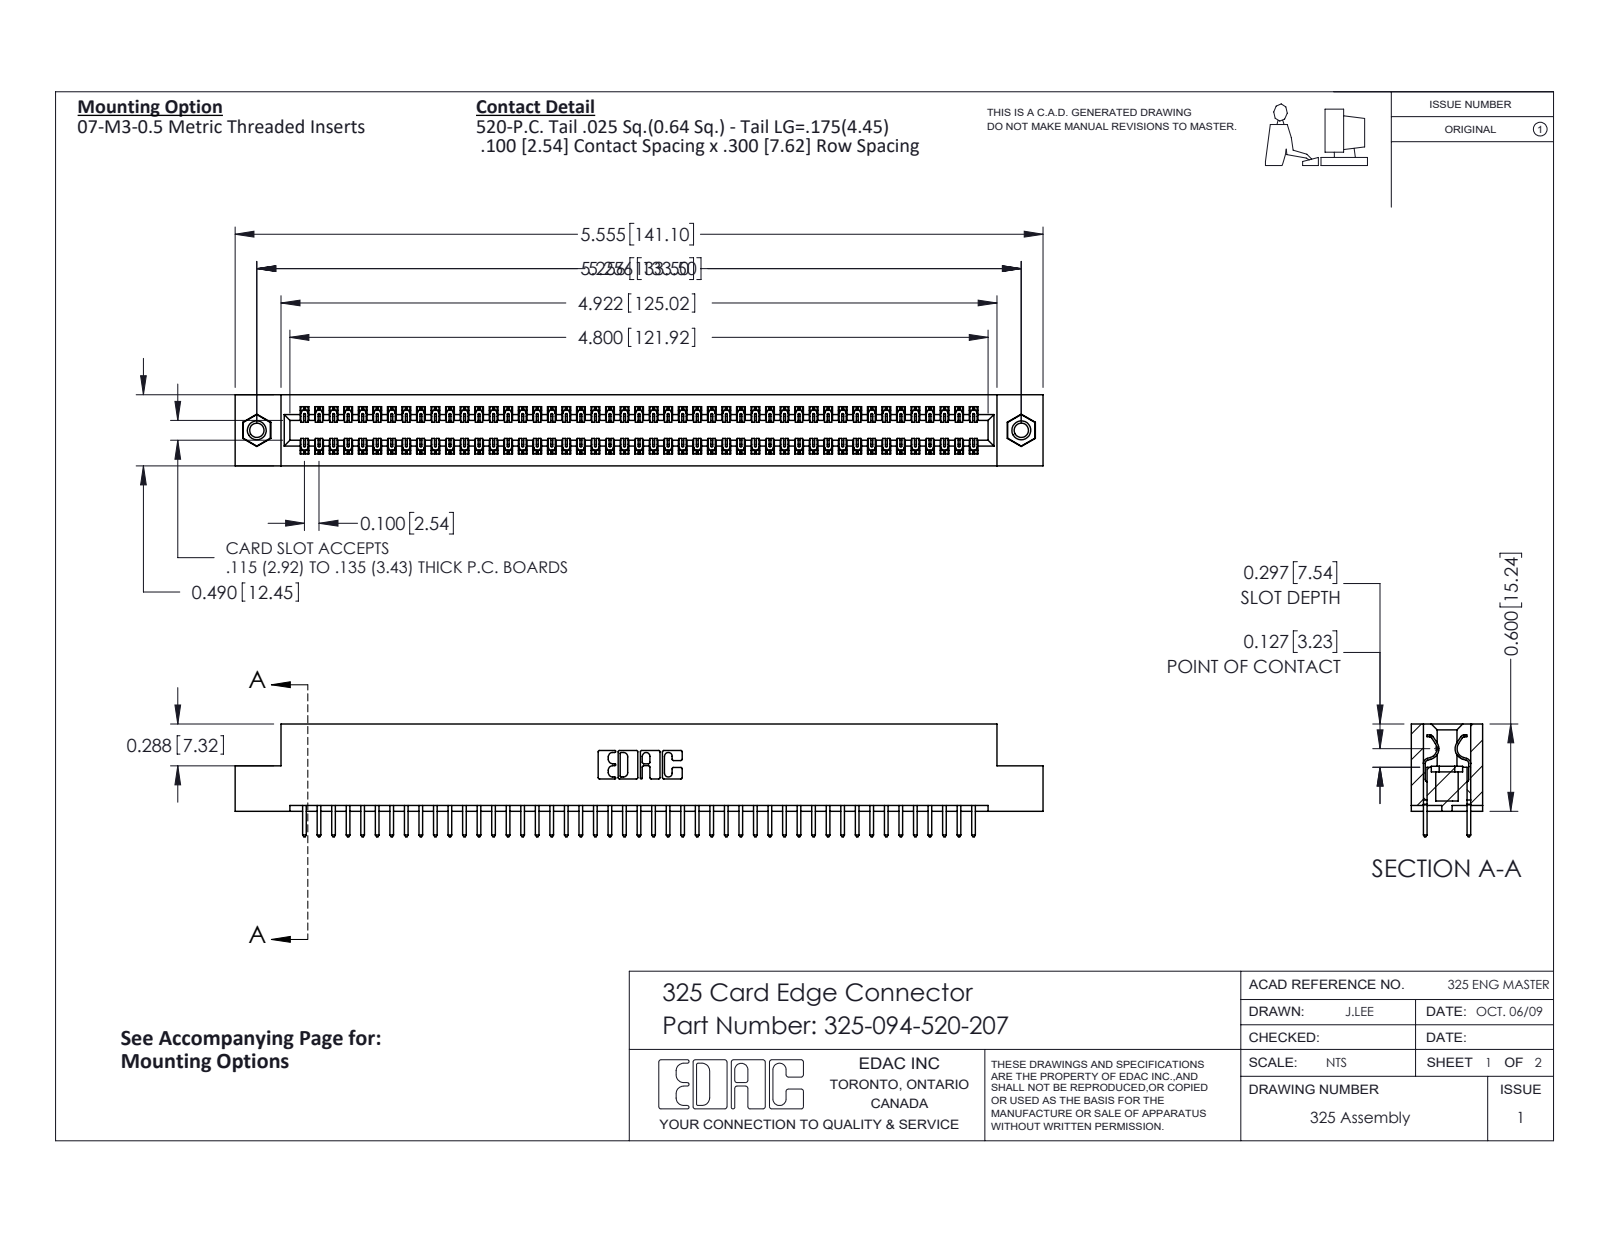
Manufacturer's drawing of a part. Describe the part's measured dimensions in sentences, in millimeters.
The part is named "325-094-520-207; 325 Part_TI; 345-250-001_345-250-005-103; 325-292-001_325-293-120". Its 3-D file was written by "SolidWorks 2016 (CONFIG_CONTROL_DESIGN)". It is 97 solids with 5062 faces: 3486 planar, 1560 cylindrical and 16 other. Overall it measures 141.1 by 19.7 by 12.4 millimeters. Its volume is 18 240 cubic millimeters and its surface area 22 030 square millimeters. Round holes: 2 of diameter 2.5, 2 of diameter 3.2, 2 of diameter 4.1. Round bosses or shafts: 2 of diameter 3.9. Partial cylindrical surfaces (rounded edges, fillets, slot ends): 141 of radius 0.2, 94 of radius 0.3, 22 of radius 0.3, 6 of radius 0.2, 6 of radius 0.8, 3 of radius 0.7, 2 of radius 0.4, 2 of radius 0.6. The main face-to-face distances are 2.1, 10.3, 7.6, 12.4, 2.7, 9.7, 0.6, 8.3, 7, 14.2. The hole center spacings are 133.5.
